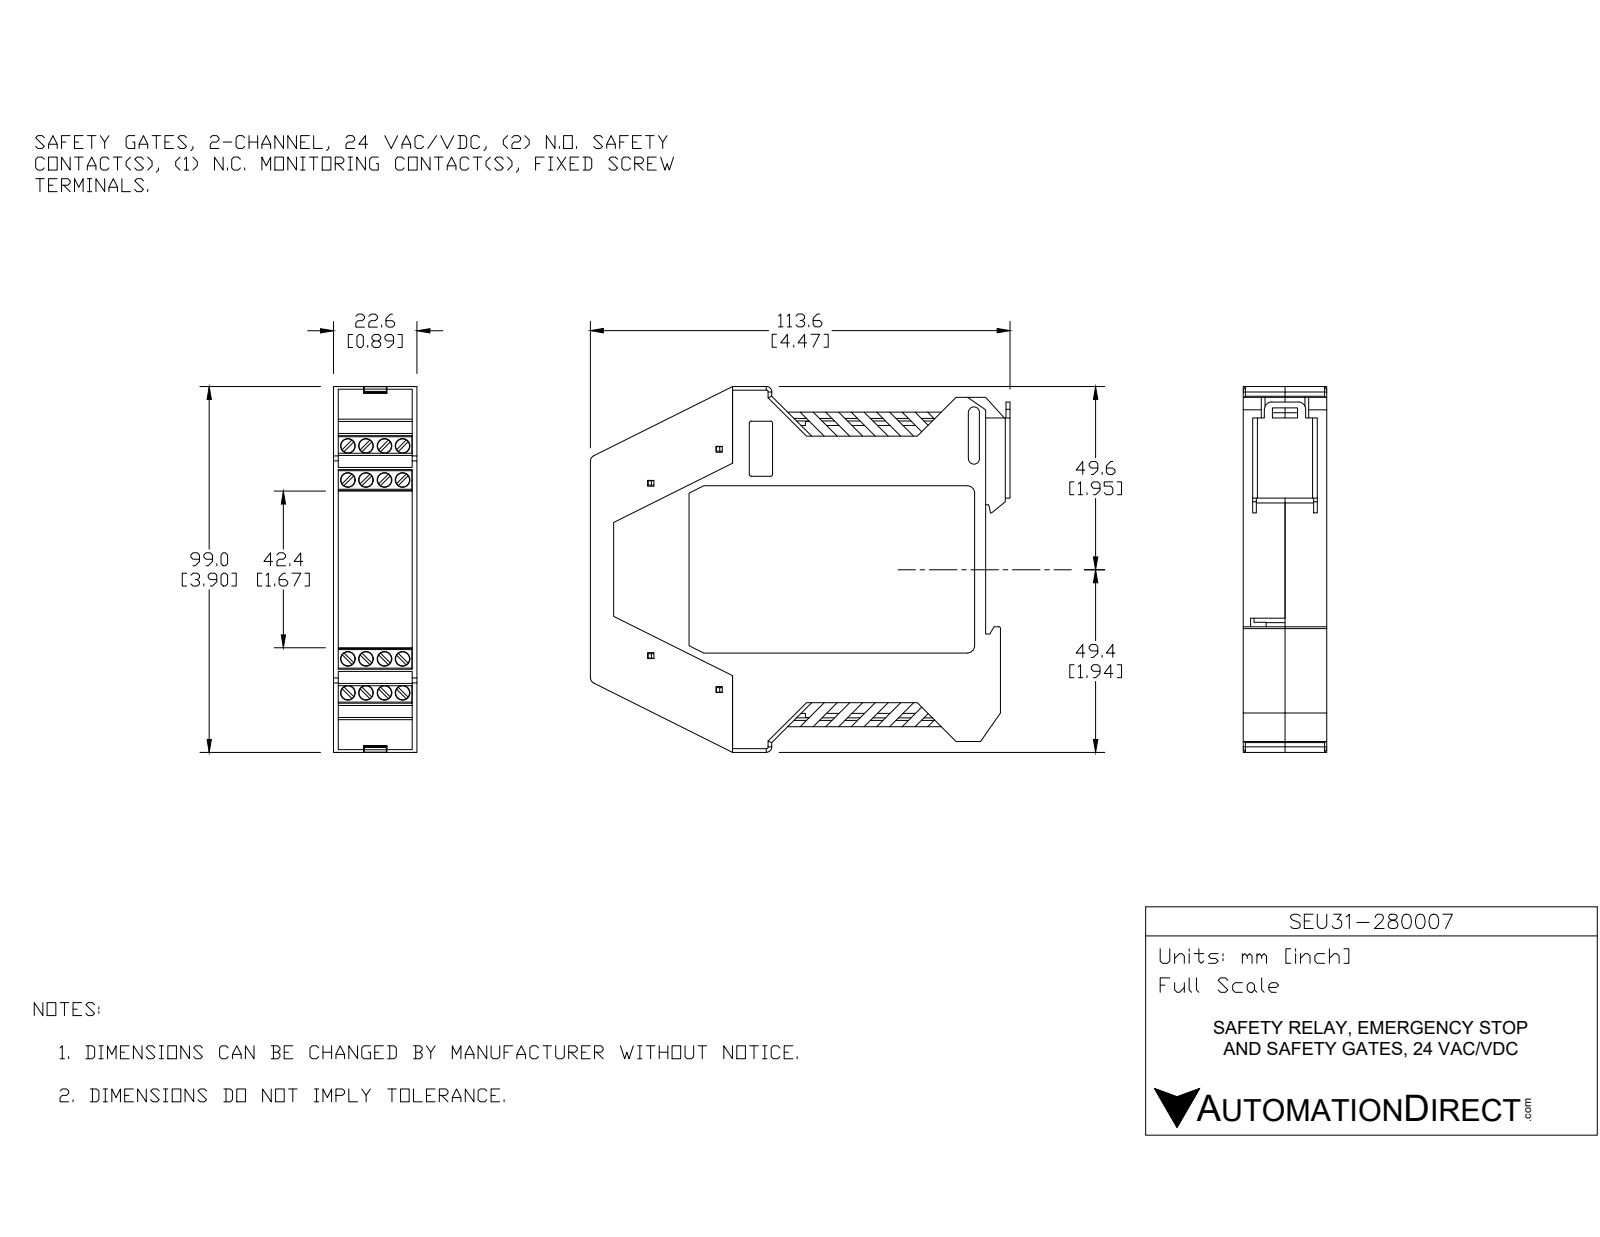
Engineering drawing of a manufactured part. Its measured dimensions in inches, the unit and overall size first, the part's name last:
Units: inches
Overall size (bounding box): 4.472 × 3.898 × 1.78
Round holes (diameter × count): ⌀0.157 ×32, ⌀0.118 ×8, ⌀0.079 ×2
Round bosses / shafts (diameter × count): ⌀0.15 ×32, ⌀0.055 ×16
Partial cylindrical surfaces — rounded edges, fillets, slot ends (radius × count): R0.02 ×57, R0.008 ×30, R0.012 ×22, R0.047 ×8, R0.059 ×8, R0.026 ×4, R0.079 ×4, R0.051 ×2
Main face-to-face distances: 0.059, 1.72, 1.713, 1.772, 0.051, 1.661, 0.89, 1.78, 0.157, 1.764
Hole centre spacings: 0.39, 0.193, 0.362, 0.41, 0.532, 0.89, 0.961, 2.26
Volume: 6.216 in³ · Surface area: 166.5 in²
Bodies: 17 solids, 3511 faces (2939 planar, 564 cylindrical, 8 other)
Part name (STEP PRODUCT): 280-Viper-44 (STEP format)
STEP written by: SolidWorks 2015 (CONFIG_CONTROL_DESIGN)
